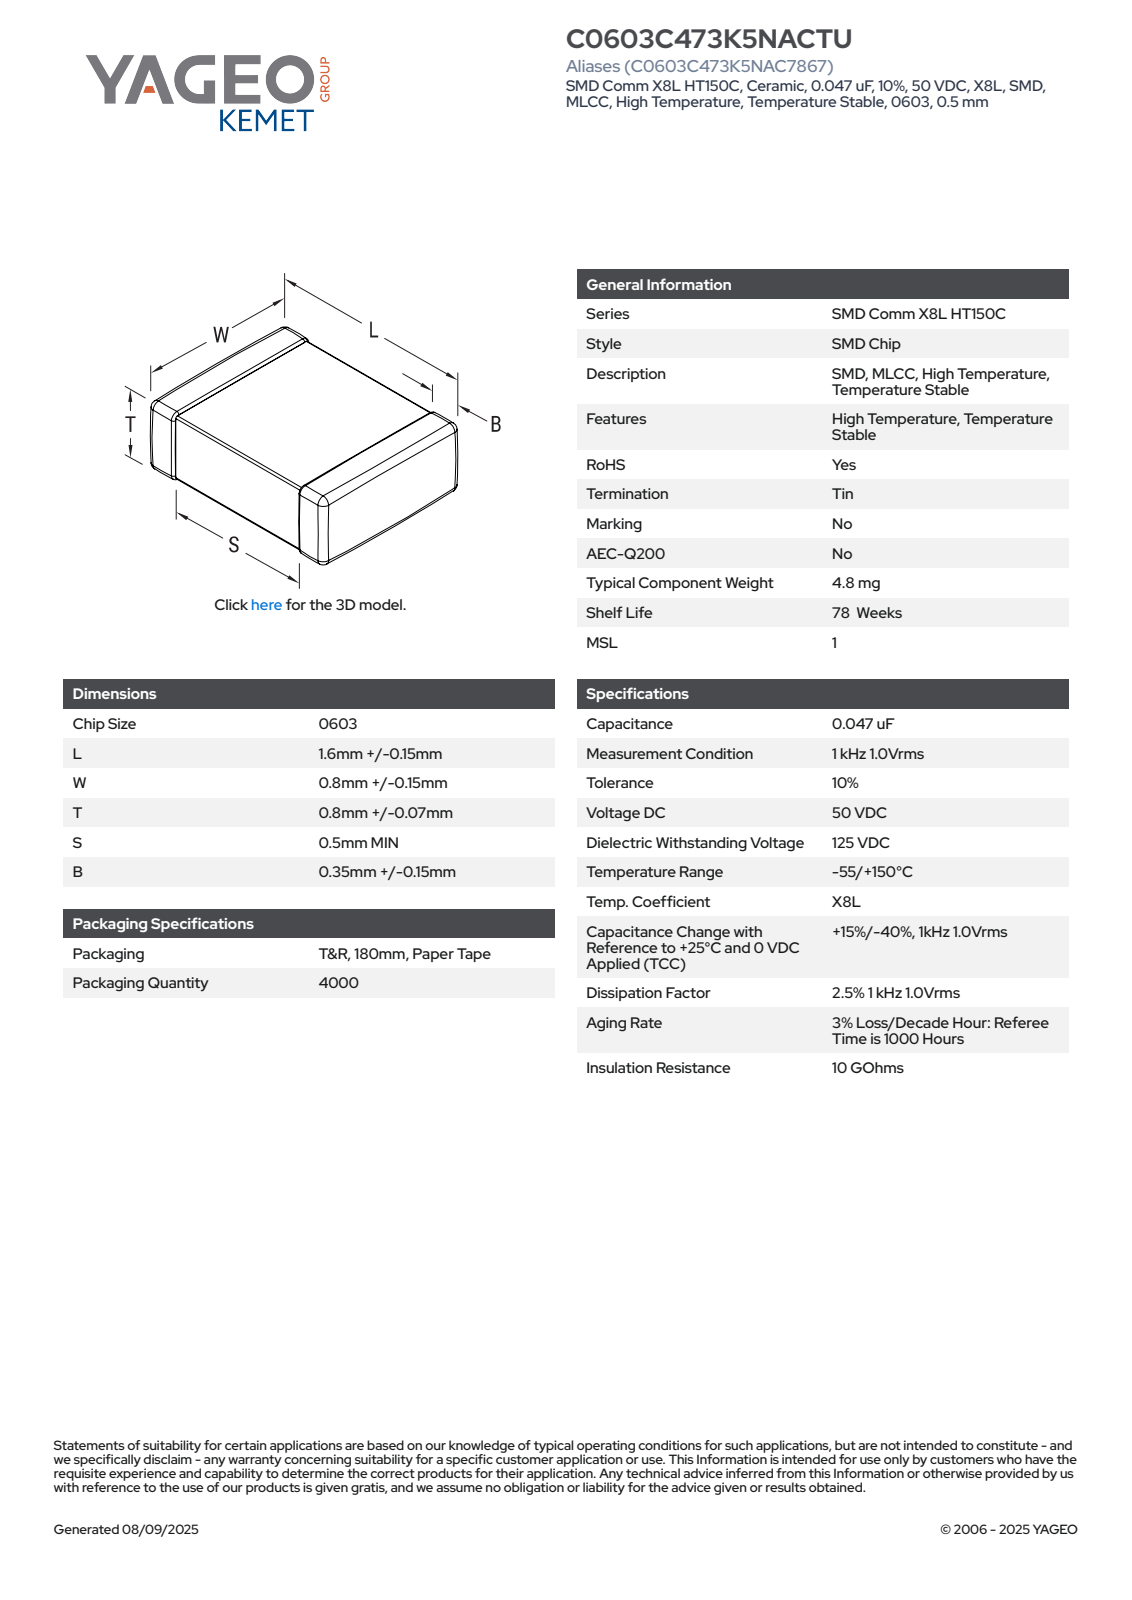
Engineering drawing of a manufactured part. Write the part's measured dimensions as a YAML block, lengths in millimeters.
part_name: "CCS_CCSTD_0603_L1.75W0.95S0.8T0.87B0.35"
step_written_by: "SolidWorks 2021 (AUTOMOTIVE_DESIGN)"
units: millimeters
bodies: {solids: 4, faces: 125, planar: 71, cylindrical: 38, other: 16}
overall_size: [1.75, 0.95, 0.87]
volume: 1
surface_area: 8
face_to_face_distances: [0.85, 0.93, 0.87, 0.95, 1.75, 0.83, 0.91, 0.86, 0.84, 0.81]
